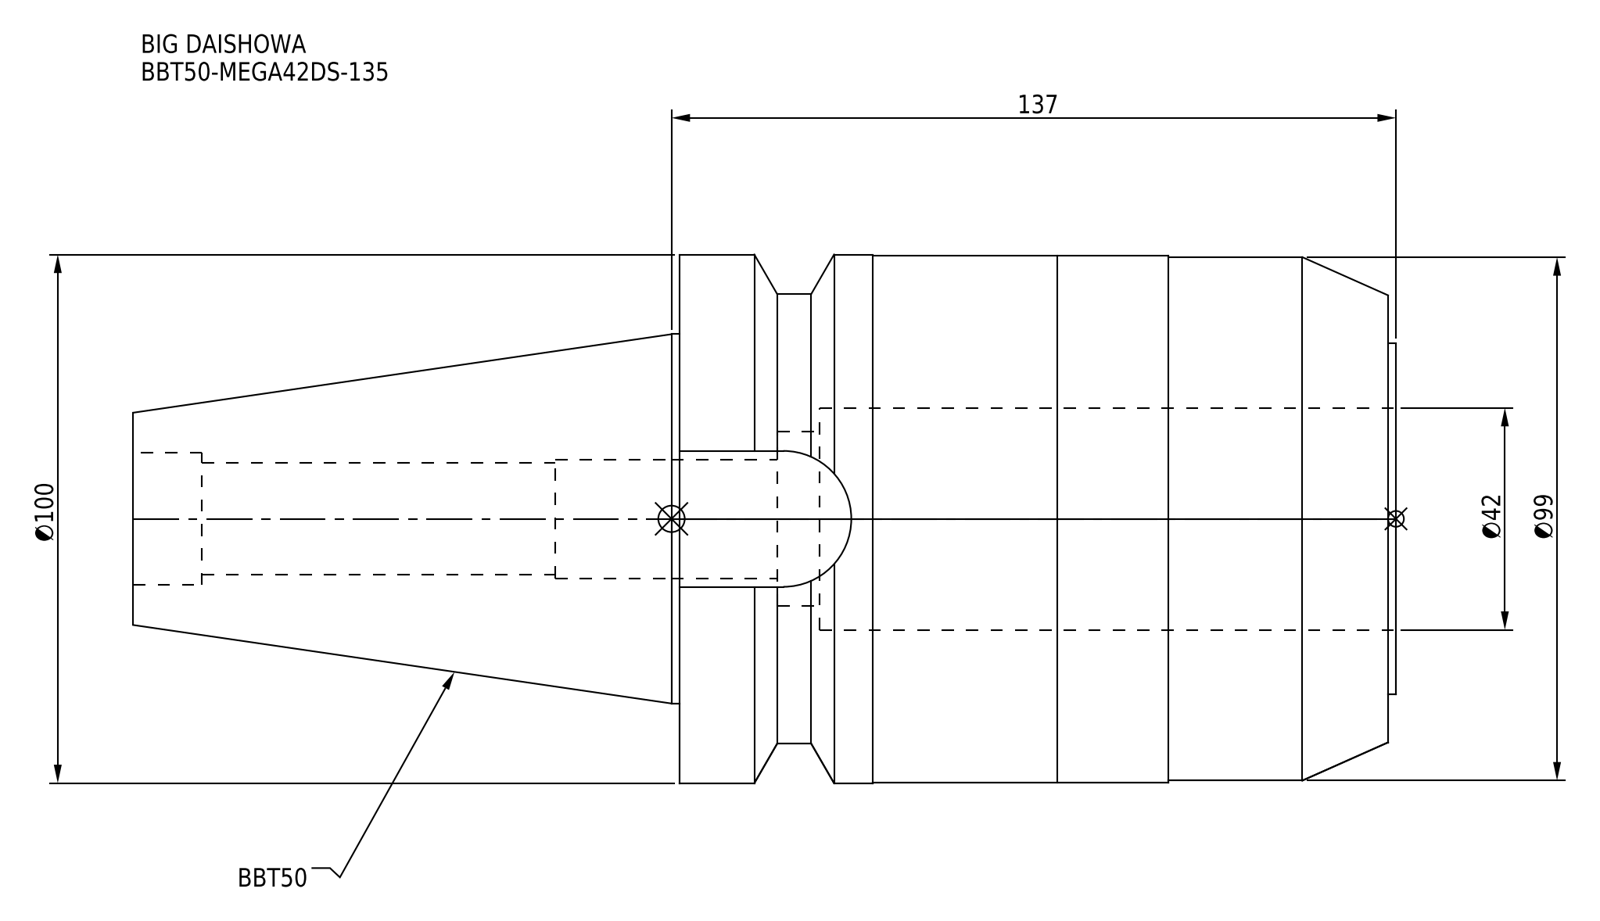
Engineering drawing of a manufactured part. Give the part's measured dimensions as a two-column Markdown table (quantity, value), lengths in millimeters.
| quantity | value |
| --- | --- |
| part name | BBT50-MEGA42DS-135 |
| STEP written by | CREO PARAMETRIC BY PTC INC, 2016380 (AUTOMOTIVE_DESIGN) |
| units | millimeters |
| bodies | 1 solid, 52 faces (16 planar, 28 cylindrical, 8 other) |
| overall size | 238.8 × 100 × 100 |
| volume | 1 039 000 mm³ |
| surface area | 97 055 mm² |
| round holes (diameter × count) | 21.2 × 1, 22.5 × 1, 25 × 1, 33 × 1, 42 × 1 |
| round bosses / shafts (diameter × count) | 100 × 1, 99.7 × 1, 99 × 1, 85 × 1, 69.85 × 1, 66.5 × 1 |
| partial cylindrical surfaces (radius × count) | 12.85 × 1 |
| main face-to-face distances | 134, 1.5, 135.5, 238.8, 237.3, 103.3, 70.8, 109, 107.5, 26.5 |
